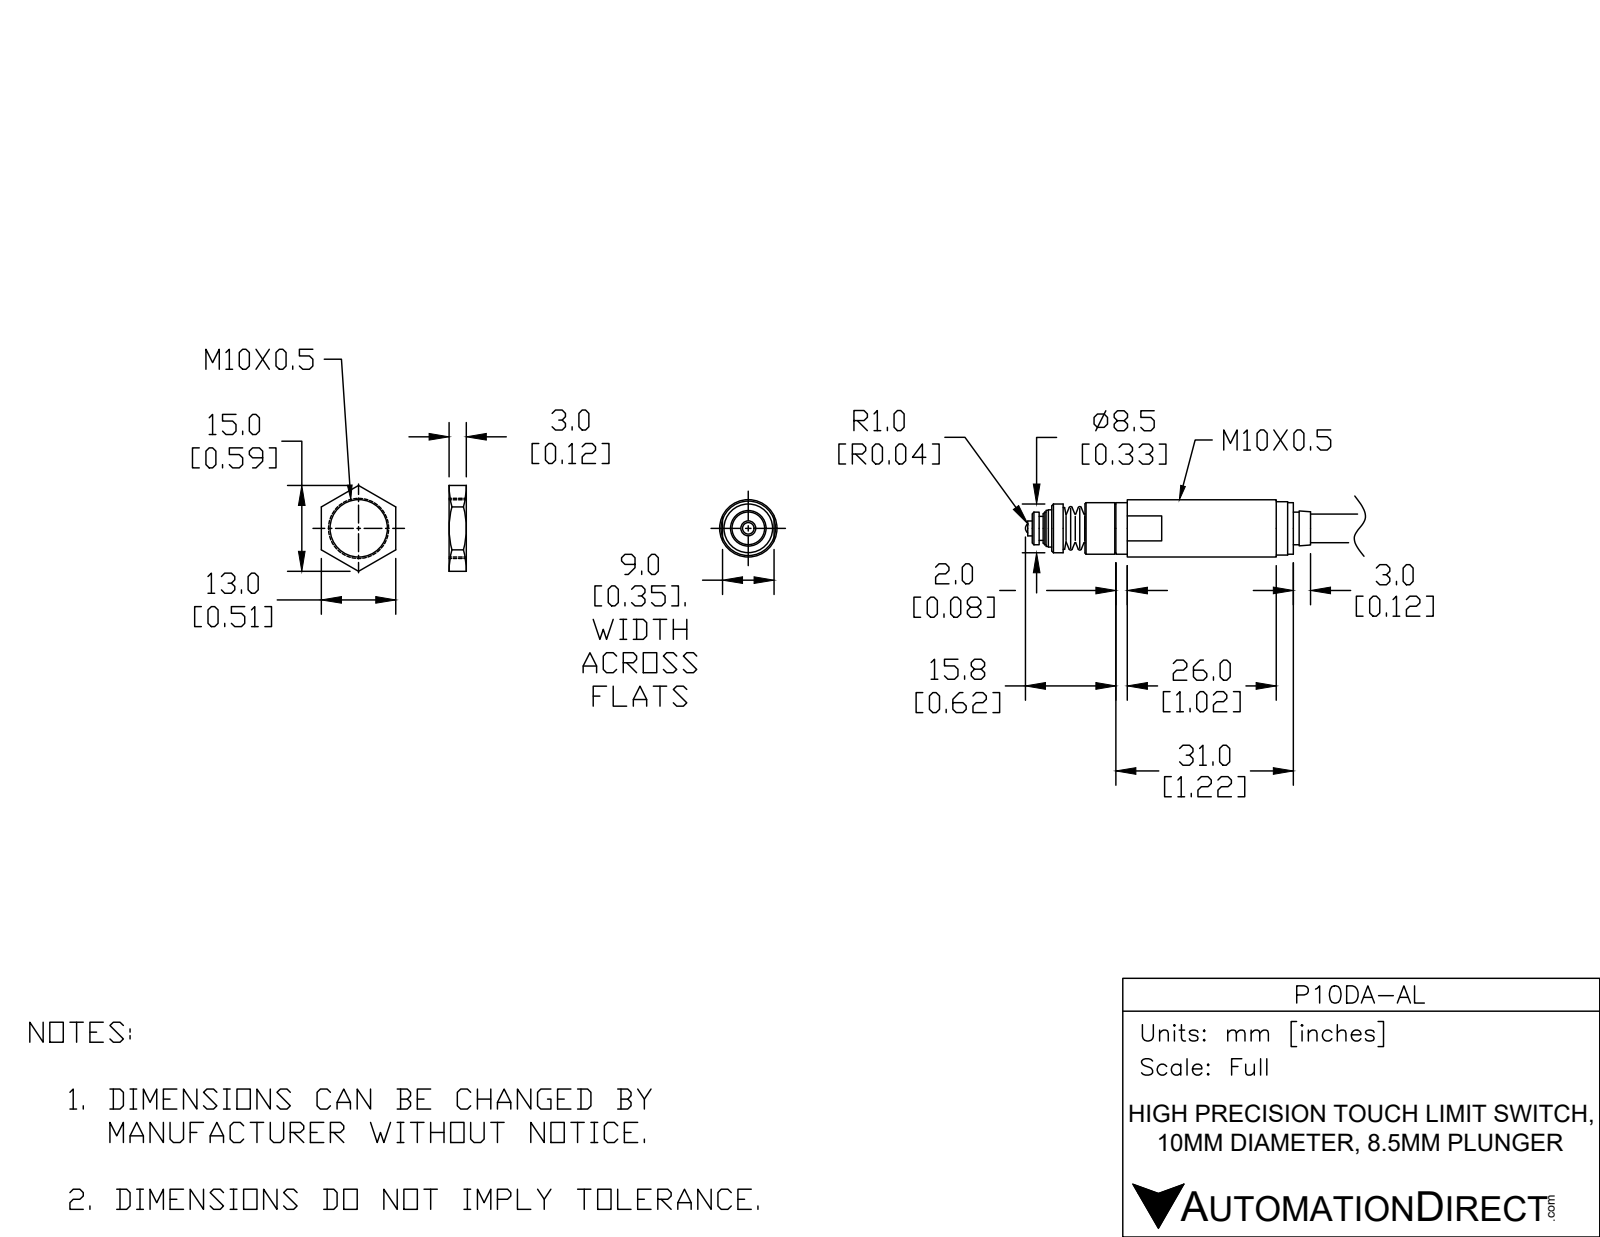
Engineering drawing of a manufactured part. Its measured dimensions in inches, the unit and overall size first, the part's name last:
Units: inches
Overall size (bounding box): 2.276 × 0.394 × 0.394
Round bosses / shafts (diameter × count): ⌀0.394 ×1, ⌀0.366 ×1, ⌀0.354 ×1, ⌀0.335 ×1, ⌀0.287 ×1, ⌀0.256 ×1, ⌀0.248 ×1, ⌀0.224 ×1
Main face-to-face distances: 1.433, 0.079, 1.866, 0.354, 1.661, 0.433, 0.362, 0.213, 1.583, 0.315
Volume: 0.191 in³ · Surface area: 3.669 in²
Bodies: 1 solid, 269 faces (23 planar, 135 cylindrical, 111 other)
Part name (STEP PRODUCT): P10DA-AL - 1
STEP written by: SolidWorks 2017 (AUTOMOTIVE_DESIGN)
